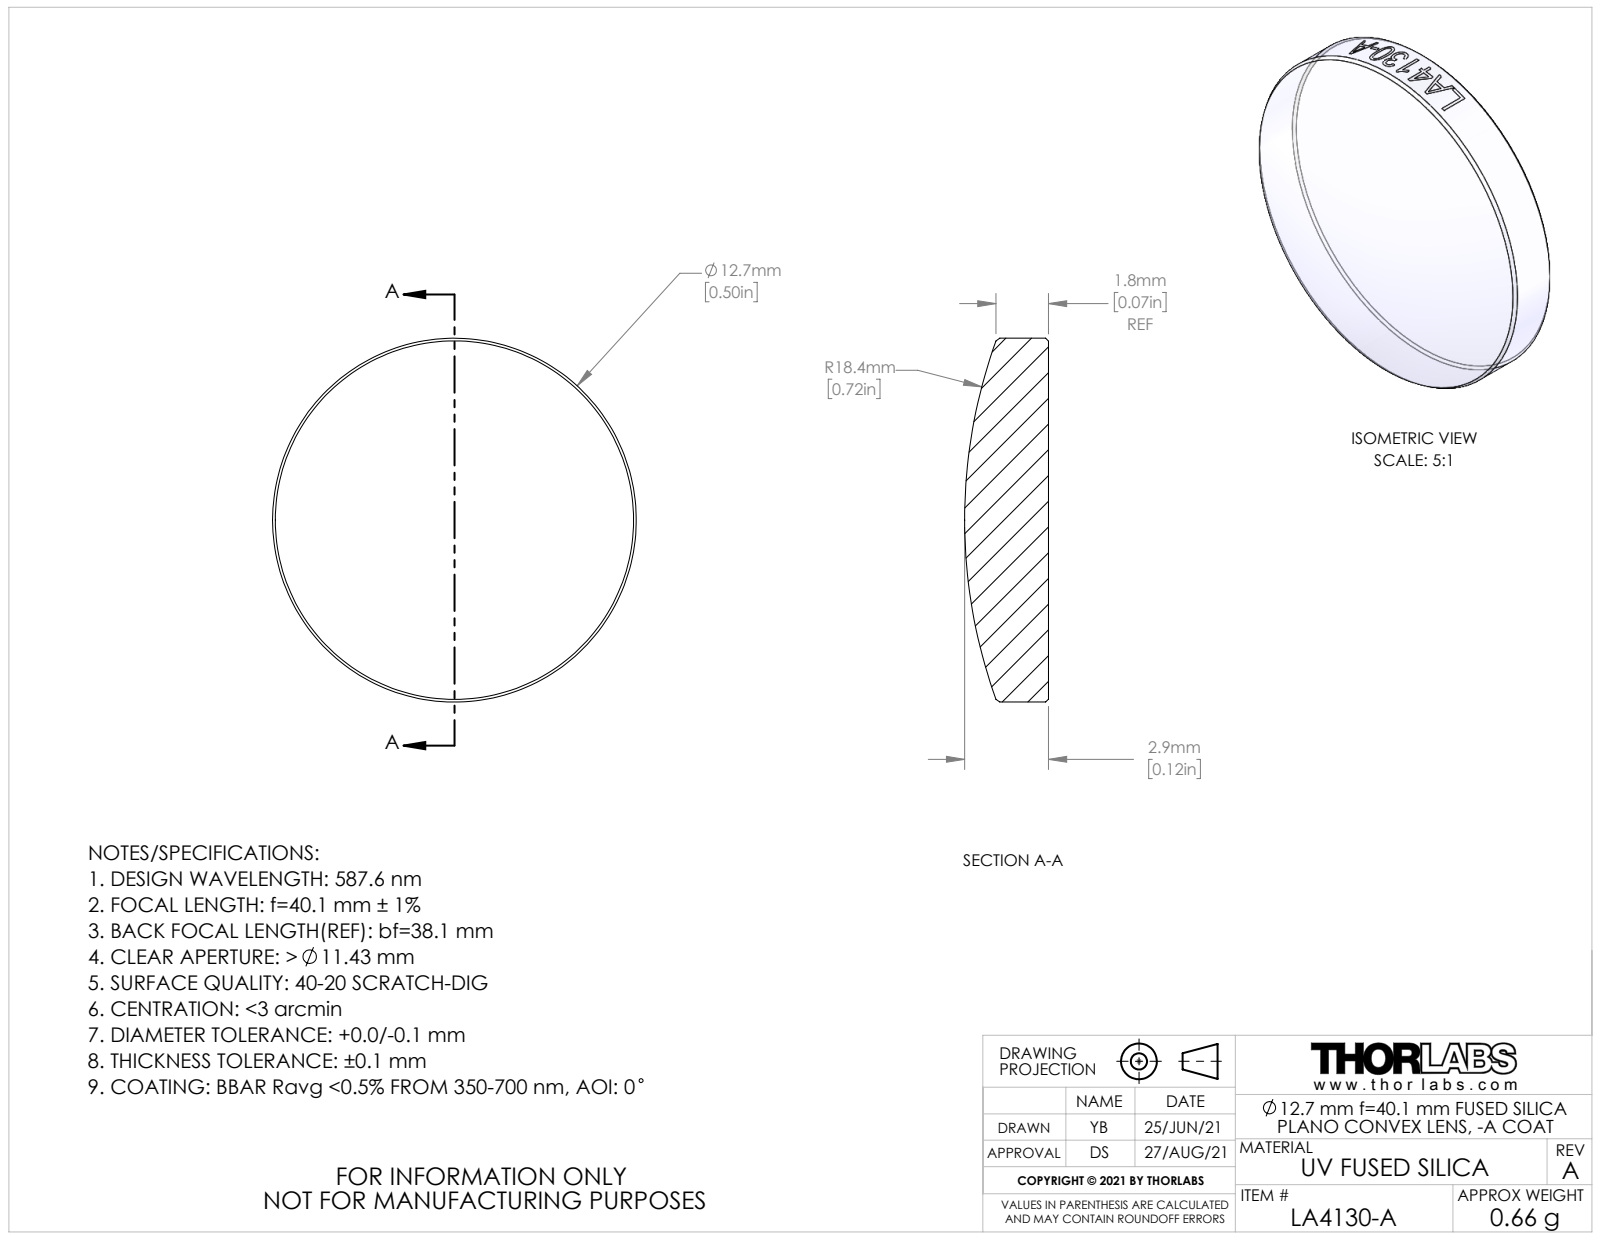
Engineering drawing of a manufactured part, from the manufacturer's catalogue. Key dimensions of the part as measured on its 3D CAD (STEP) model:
Part name (STEP PRODUCT): CTN017555; CTN017525-E0W
STEP written by: SolidWorks 2018 (AUTOMOTIVE_DESIGN)
Units: millimetres
Bodies: 1 solid, 21 faces (1 planar, 14 cylindrical, 6 other)
Overall size (bounding box): 12.7 × 12.7 × 2.93
Volume: 300 mm³ · Surface area: 325 mm²
Round bosses / shafts (diameter × count): ⌀12.7 ×1
